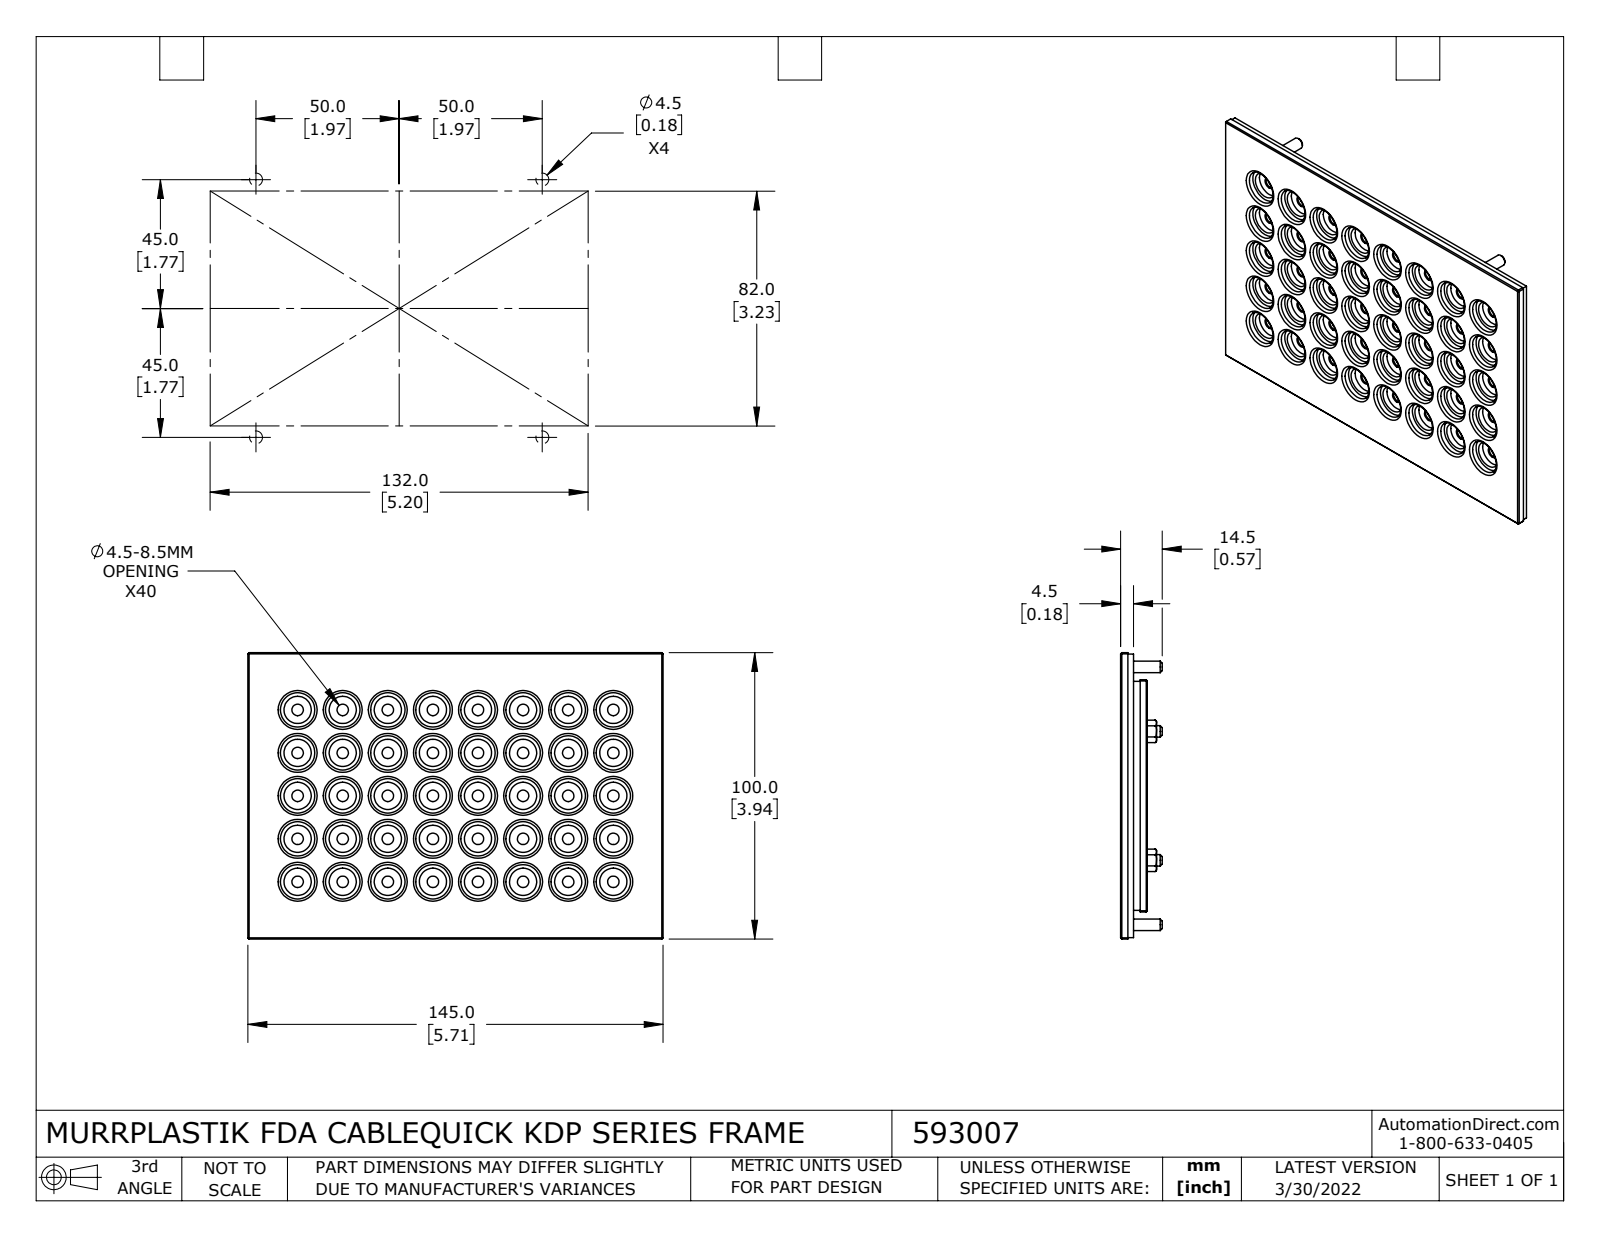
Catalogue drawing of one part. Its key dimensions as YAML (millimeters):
part_name: "593007"
step_written_by: "SolidWorks 2021 (CONFIG_CONTROL_DESIGN)"
units: millimeters
bodies: {solids: 1, faces: 866, planar: 288, cylindrical: 372, other: 206}
overall_size: [145, 100, 14.5]
volume: 84900
surface_area: 44680
round_holes:
  - {diameter: 4, count: 40}
  - {diameter: 9.5, count: 40}
  - {diameter: 12, count: 40}
  - {diameter: 13, count: 40}
  - {diameter: 5.5, count: 8}
  - {diameter: 4.5, count: 4}
round_bosses_or_shafts:
  - {diameter: 4, count: 8}
partial_cylinders:
  - {radius: 6, count: 4}
face_to_face_distances: [6.8, 4.5, 2.5, 2.3, 4.8, 9.3, 4.3, 0.5, 2, 9.5]
hole_center_spacings: [34.9, 15, 21.7, 64.8, 31.5, 43.5, 49.6, 21.8]
